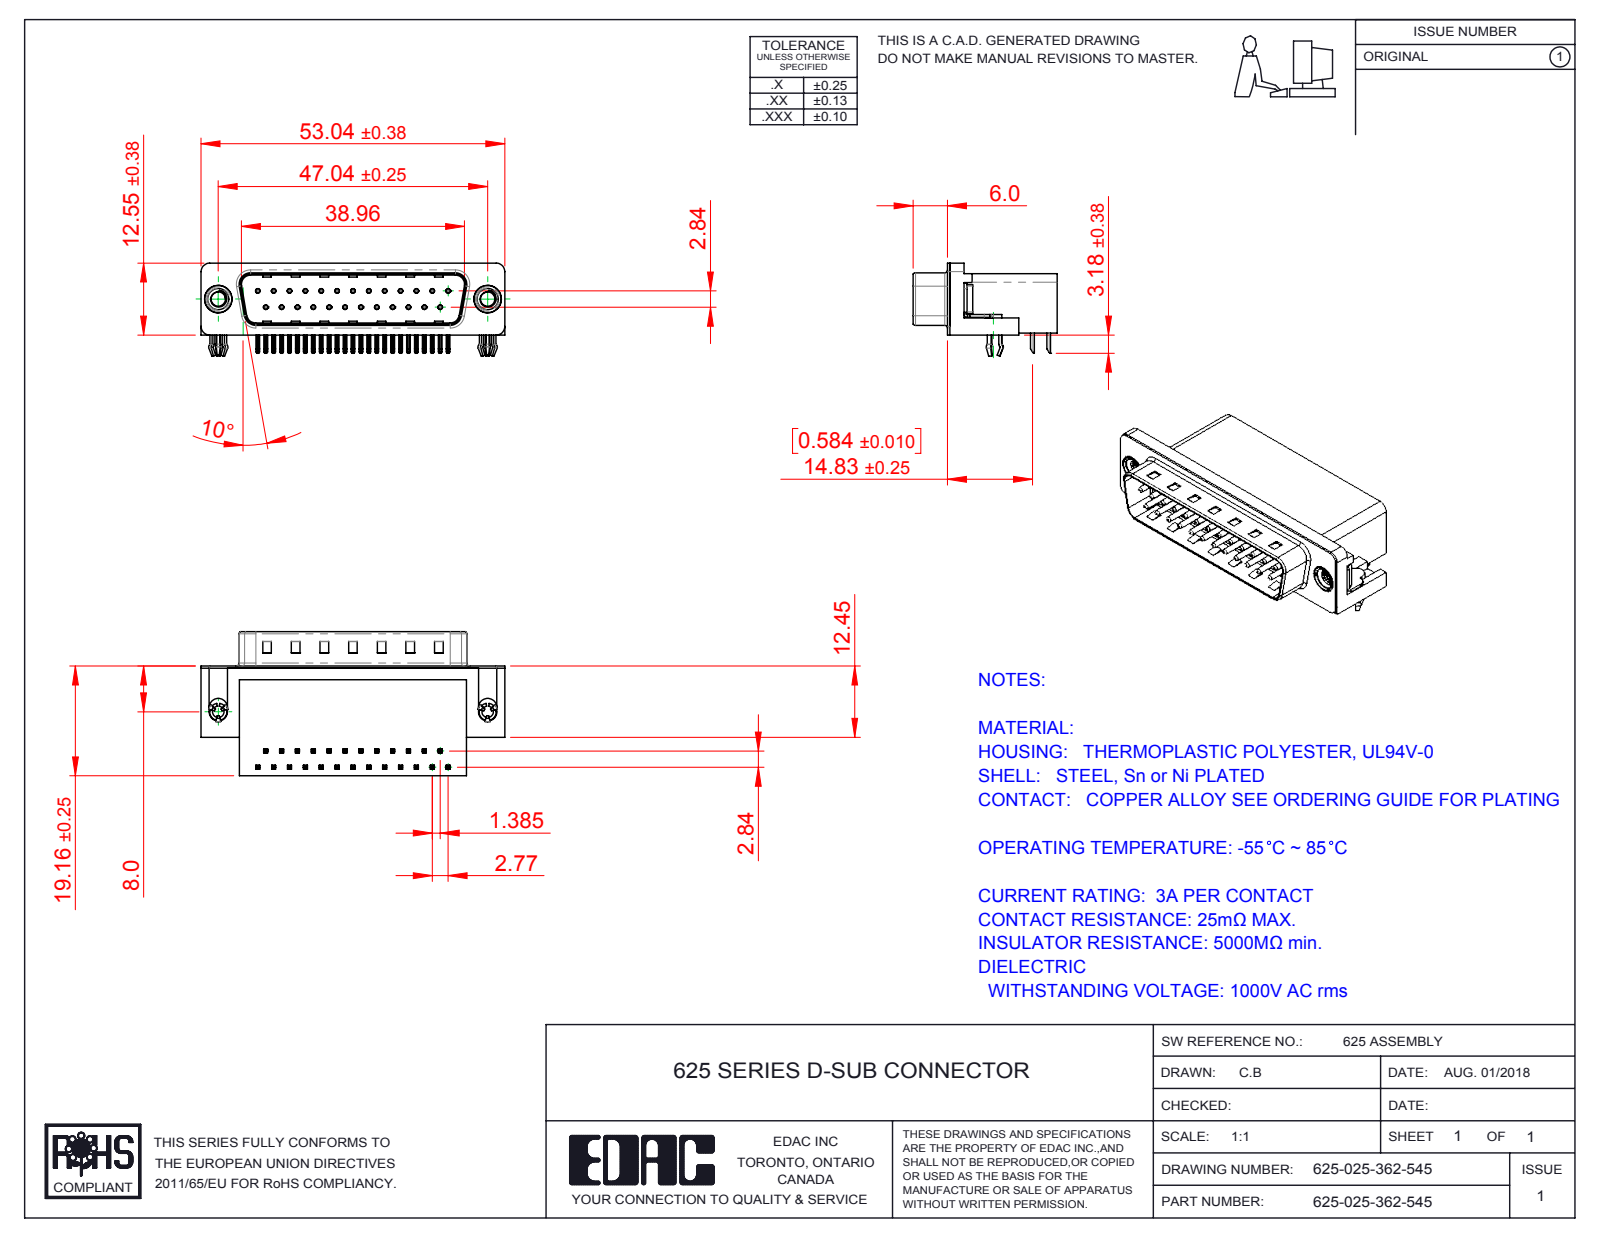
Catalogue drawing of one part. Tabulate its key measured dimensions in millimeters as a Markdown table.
| quantity | value |
| --- | --- |
| part name | 625 M3 Threaded Rivet; 625 Housing_25 Socket; 625 Contact Bottom; 625 Shell_25 Socket (+3 more) |
| STEP written by | SolidWorks 2016 (CONFIG_CONTROL_DESIGN) |
| units | millimeters |
| bodies | 31 solids, 2369 faces (1443 planar, 671 cylindrical, 255 other) |
| overall size | 53.04 × 25.16 × 16.25 |
| volume | 9 167 mm³ |
| surface area | 8 926 mm² |
| round holes (diameter × count) | 0.35 × 25, 0.8 × 25, 2 × 2, 2.5 × 2, 4 × 2, 4.8 × 2, 5 × 2 |
| round bosses / shafts (diameter × count) | 0.75 × 25, 4.9 × 2, 4.75 × 2, 3.9 × 2, 3 × 2 |
| partial cylindrical surfaces (radius × count) | 0.25 × 112, 0.12 × 50, 1 × 16, 0.5 × 9, 1.6 × 8, 1.5 × 7, 0.9 × 4, 2 × 4 |
| main face-to-face distances | 0.4, 10.35, 18.76, 2.1, 8.76, 10.46, 10.86, 1.7, 19.16, 10.11 |
| hole center spacings | 3.16, 2.77, 11.08, 5.54, 8.31, 5.03, 13.85, 7.48 |
